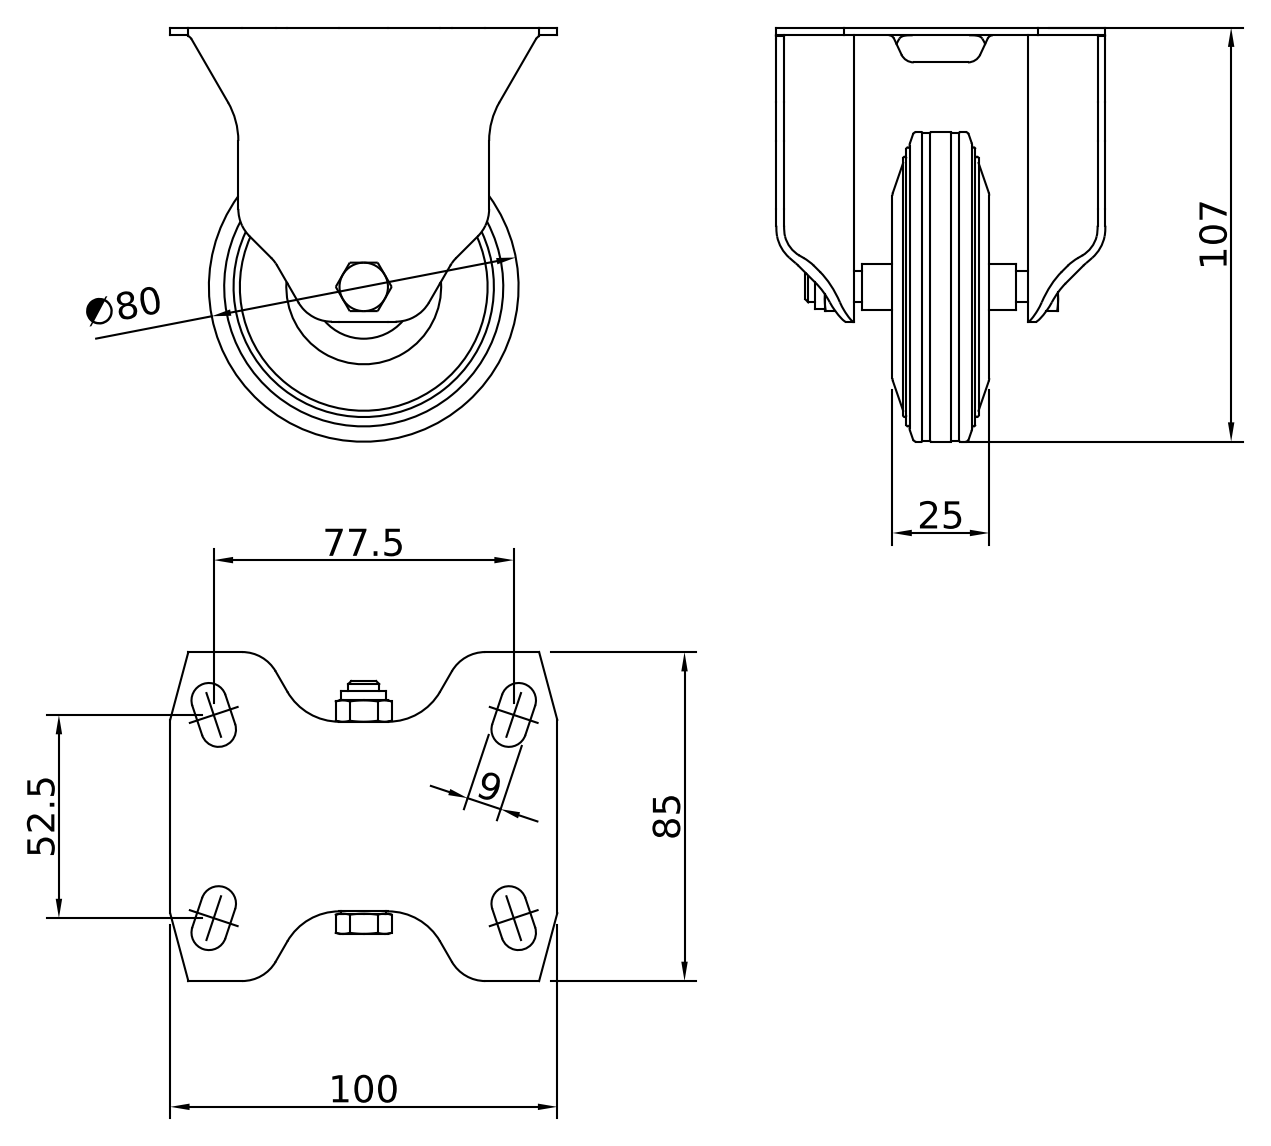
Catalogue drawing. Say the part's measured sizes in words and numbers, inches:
The part is named "CRUST0000020; 440000025823; 440000025822; 440000025821". Its 3-D file was written by "Autodesk Inventor 2022 (AUTOMOTIVE_DESIGN)". It is 3 solids with 242 faces: 101 planar, 78 cylindrical and 63 other. Overall it measures 4.213 by 3.937 by 3.346 inches. Its volume is 8.469 cubic inches and its surface area 89.76 square inches. Round holes: 1 of diameter 0.354, 1 of diameter 0.472. Round bosses or shafts: 1 of diameter 3.15, 1 of diameter 3.13, 1 of diameter 0.458, 1 of diameter 0.315. Partial cylindrical surfaces (rounded edges, fillets, slot ends): 10 of radius 0.394, 8 of radius 0.059, 8 of radius 0.138, 8 of radius 0.177, 4 of radius 0.276, 4 of radius 0.315, 4 of radius 0.61, 4 of radius 0.689. The main face-to-face distances are 0.079, 1.85, 0.394, 0.472, 1.457, 1.378, 0.709, 2.559, 0.276, 0.154.
